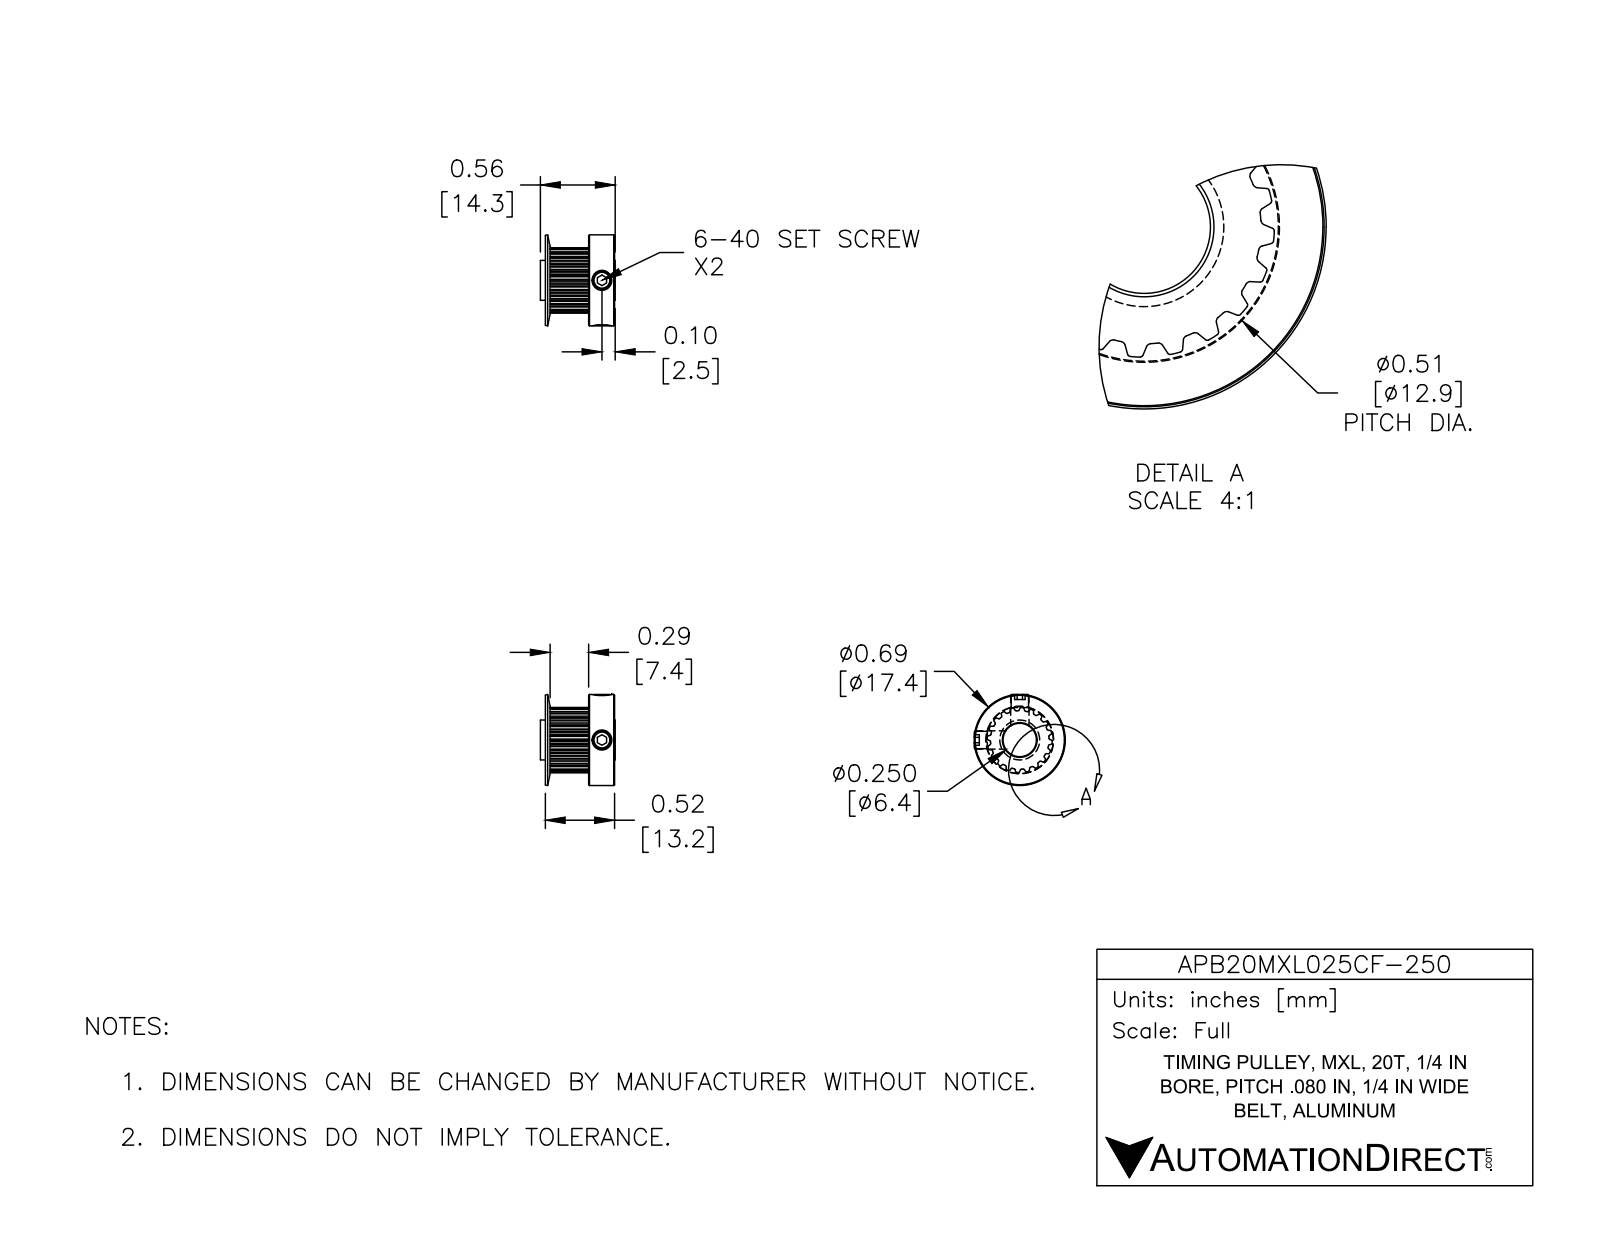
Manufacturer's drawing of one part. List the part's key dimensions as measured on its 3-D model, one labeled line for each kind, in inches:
Part name (STEP PRODUCT): APB20MXL025CF-250
STEP written by: SolidWorks 2016 (AUTOMOTIVE_DESIGN)
Units: inches
Bodies: 3 solids, 237 faces (64 planar, 151 cylindrical, 22 other)
Overall size (bounding box): 0.685 × 0.685 × 0.563
Volume: 0.1 in³ · Surface area: 2.835 in²
Round holes (diameter × count): ⌀0.138 ×2, ⌀0.25 ×1
Round bosses / shafts (diameter × count): ⌀0.13 ×2, ⌀0.685 ×1, ⌀0.3 ×1
Partial cylindrical surfaces — rounded edges, fillets, slot ends (radius × count): R0.005 ×40, R0.009 ×40, R0.22 ×1, R0.245 ×1
Main face-to-face distances: 0.194, 0.309, 0.504, 0.184, 0.019, 0.29, 0.485, 0.054, 0.073, 0.363
